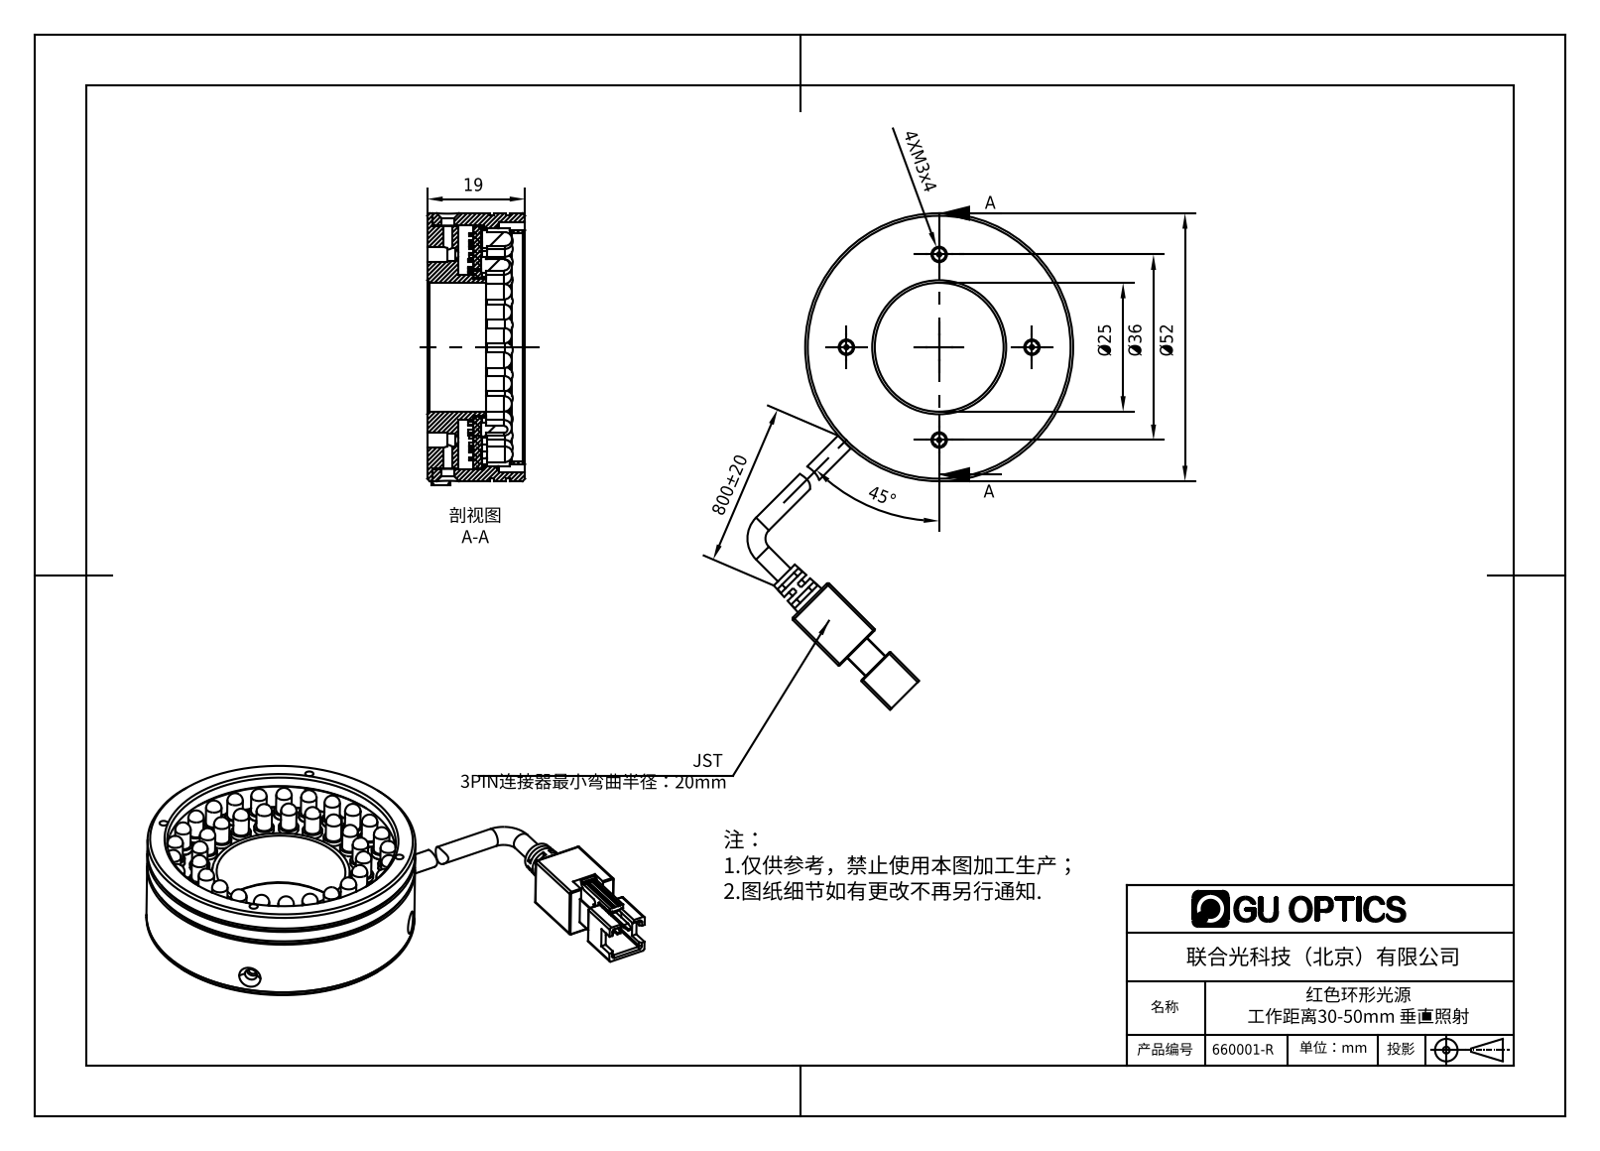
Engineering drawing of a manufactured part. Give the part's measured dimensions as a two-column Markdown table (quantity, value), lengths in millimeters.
| quantity | value |
| --- | --- |
| part name | 660001-R |
| STEP written by | SolidWorks 2016 (AUTOMOTIVE_DESIGN) |
| units | millimeters |
| bodies | 53 solids, 1320 faces (770 planar, 437 cylindrical, 113 other) |
| overall size | 96.36 × 63.22 × 21.35 |
| volume | 21 232 mm³ |
| surface area | 21 563 mm² |
| round holes (diameter × count) | 3.8 × 48, 1.6 × 6, 2.5 × 4, 3 × 4, 2.4 × 2, 25 × 1, 27 × 1, 44.4 × 1, 46.2 × 1, 47.2 × 1 |
| round bosses / shafts (diameter × count) | 3 × 48, 3.5 × 2, 52 × 1, 51 × 1, 47.1 × 1, 47 × 1, 28 × 1, 26.7 × 1 |
| partial cylindrical surfaces (radius × count) | 0.1 × 15, 0.2 × 13, 0.4 × 12, 0.3 × 1, 0.68 × 1, 1.4 × 1, 1.75 × 1, 8 × 1 |
| main face-to-face distances | 3, 1, 9, 6, 5, 4.6, 1.6, 10.6, 8, 10 |
| hole center spacings | 16, 4.77, 25.02, 31.91, 9.43, 13.88, 27.71, 18.03 |
